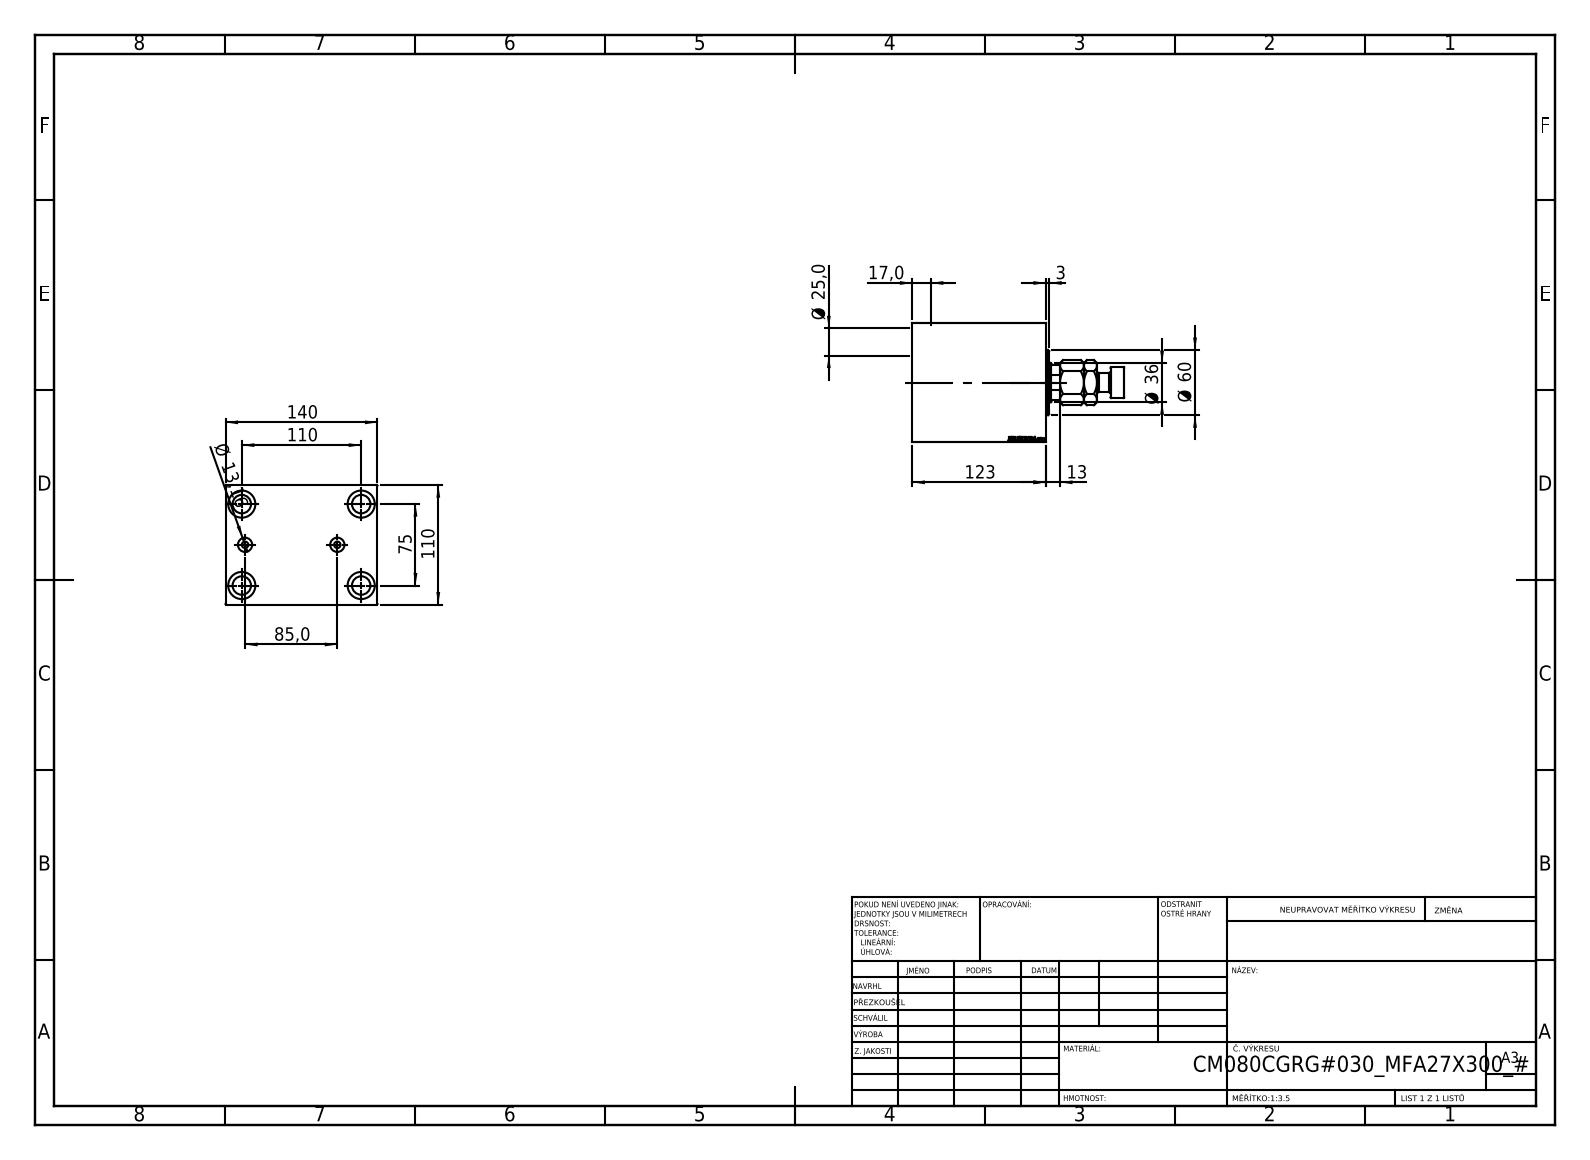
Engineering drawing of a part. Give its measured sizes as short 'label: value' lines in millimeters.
name: V450CM_VC_B; V450CM_C_Body; MFA; V450CM_C_VCP
written by: SolidWorks 2019 (CONFIG_CONTROL_DESIGN)
unit: mm
bodies: 4 solids, 912 faces (424 planar, 62 cylindrical, 426 other)
size: 195 × 140 × 110
volume: 1 747 000 mm³; area: 187 104 mm²
holes: 4× ⌀17, 4× ⌀25, 2× ⌀6, 2× ⌀13.16, 1× ⌀25.5, 1× ⌀36, 1× ⌀39.5, 1× ⌀80, 1× ⌀82, 1× ⌀87
bosses: 1× ⌀60, 1× ⌀28, 1× ⌀18
rounds: 1× R17.5
face distances: 110, 140, 123, 72, 51, 10, 21.6, 29.4, 101.4, 91.4
hole spacings: 66.57, 37.62, 43.48, 75, 95.66, 110, 113.38, 133.14
